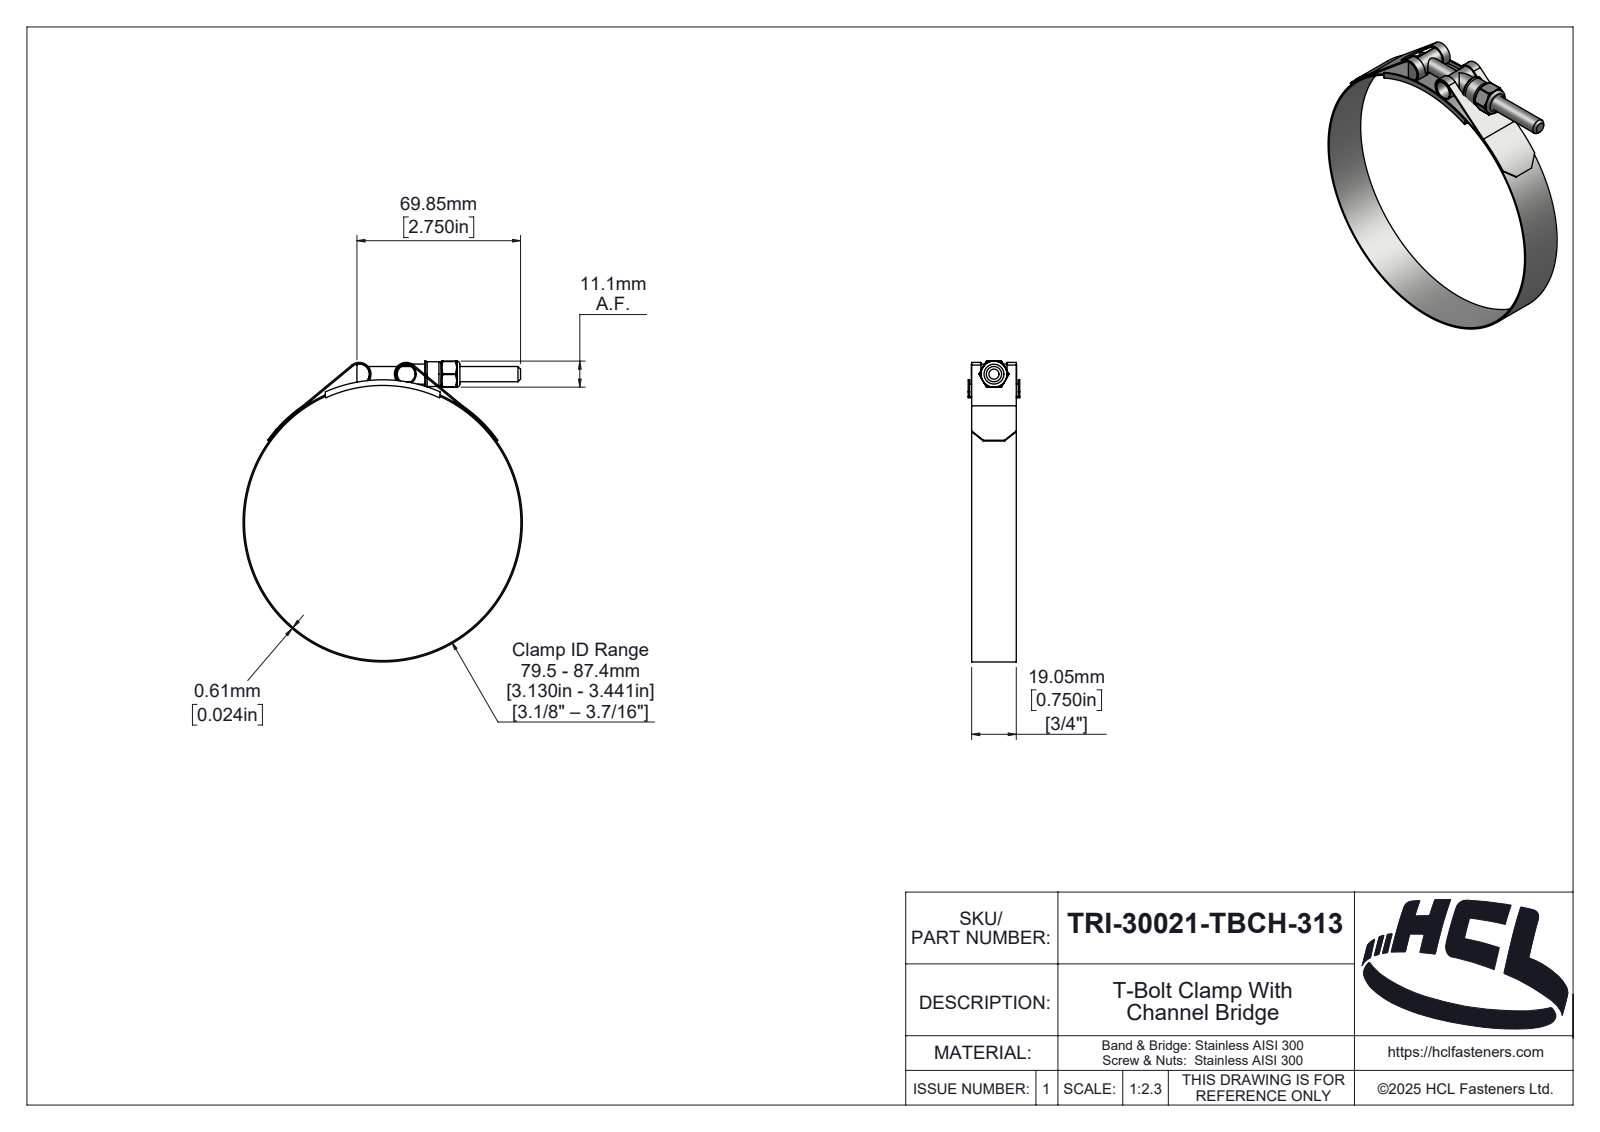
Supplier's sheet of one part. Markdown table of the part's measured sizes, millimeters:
| quantity | value |
| --- | --- |
| part name | TRI-30021-TBCH-313 |
| STEP written by | SolidWorks 2025 (AUTOMOTIVE_DESIGN) |
| units | millimeters |
| bodies | 6 solids, 330 faces (46 planar, 122 cylindrical, 162 other) |
| overall size | 128.54 × 119.22 × 22 |
| volume | 10 219 mm³ |
| surface area | 24 903 mm² |
| round holes (diameter × count) | 5.4 × 1, 6.35 × 1, 6.5 × 1, 7.58 × 1, 118 × 1 |
| round bosses / shafts (diameter × count) | 8.58 × 2, 119.22 × 1, 10.58 × 1 |
| partial cylindrical surfaces (radius × count) | 0.39 × 6, 0.5 × 2, 4.39 × 2, 5 × 2, 0.59 × 1, 2.42 × 1, 3.03 × 1, 3.19 × 1 |
| main face-to-face distances | 0.61, 19.06, 1.47, 20.53, 21.39, 0.86, 19.92, 0.74, 22, 11.11 |
| hole center spacings | 64 |
